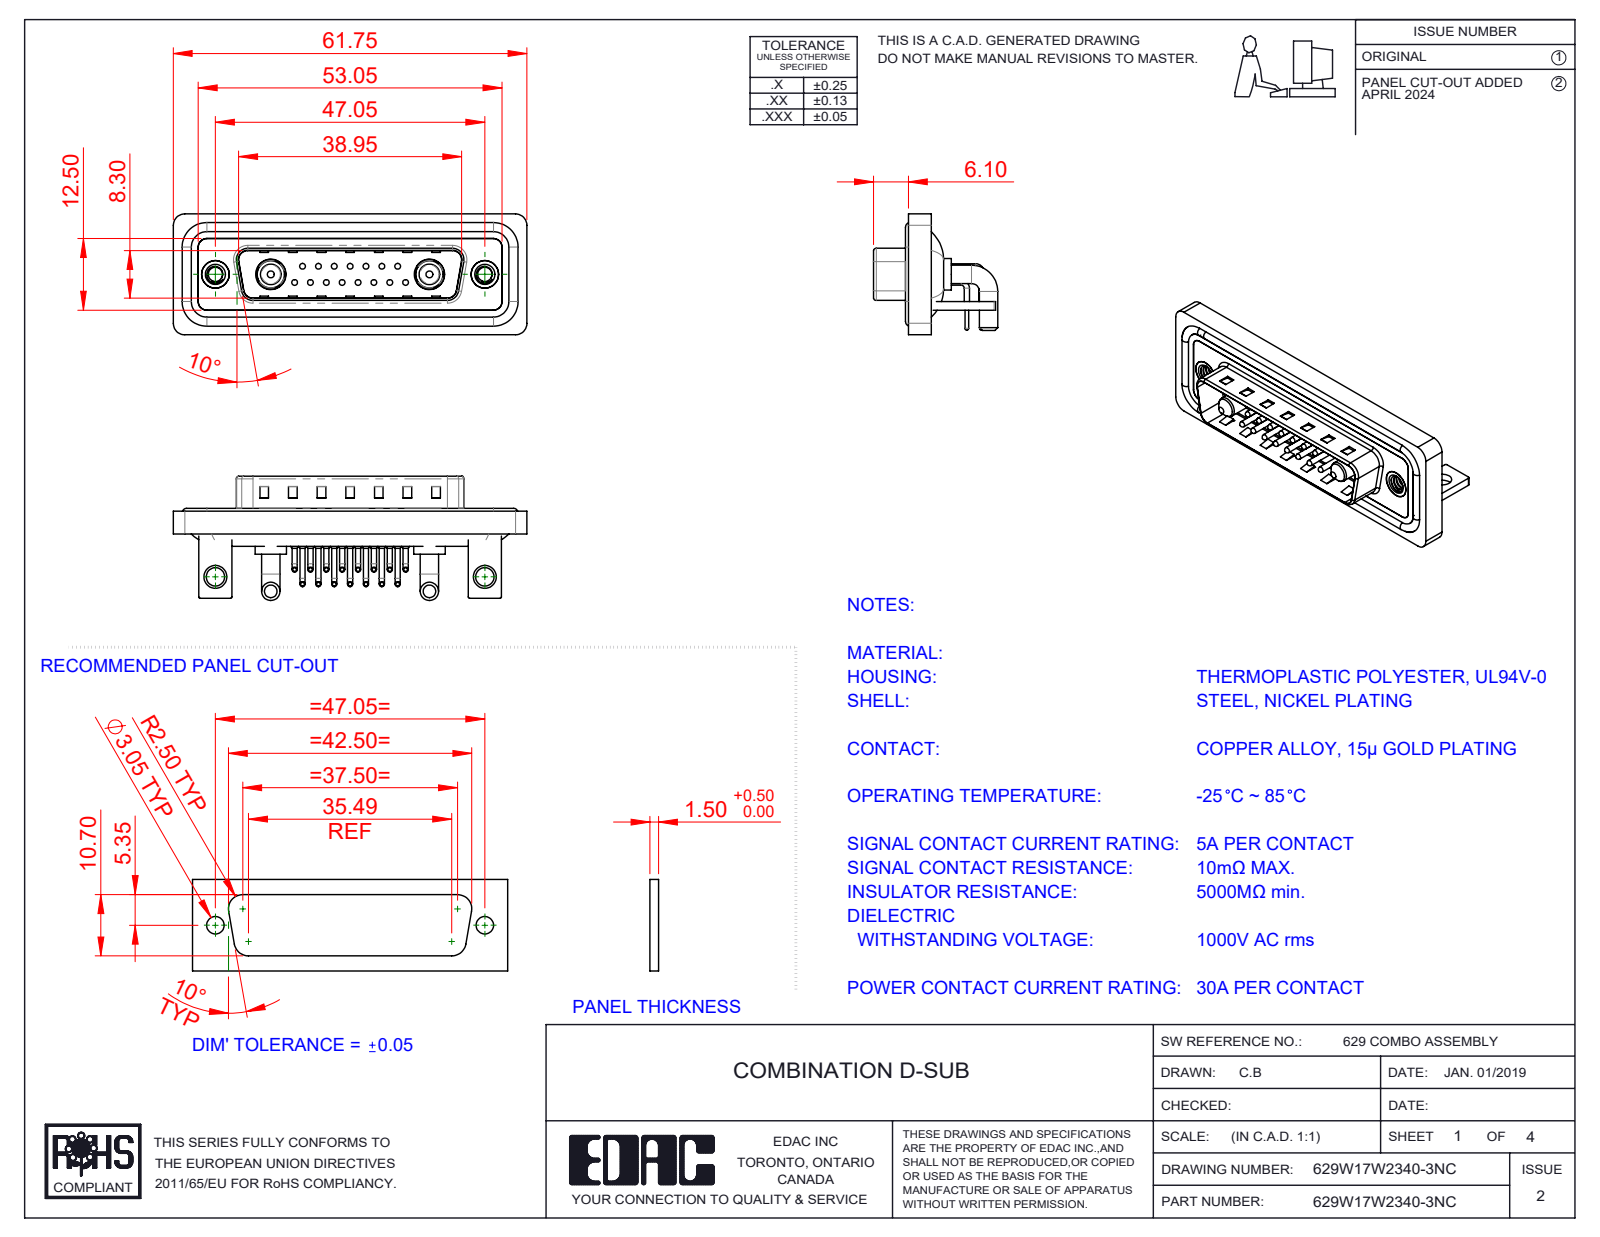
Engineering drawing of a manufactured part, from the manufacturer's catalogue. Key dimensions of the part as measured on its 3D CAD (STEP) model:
Part name (STEP PRODUCT): 629Combo Shell Front_25 Contacts; Power Pin_30A RA; 629Combo Stabilizer Bracket; 629Combo Contact Row 2 (+6 more)
STEP written by: SolidWorks 2023 (CONFIG_CONTROL_DESIGN)
Units: millimetres
Bodies: 28 solids, 2257 faces (1209 planar, 788 cylindrical, 260 other)
Overall size (bounding box): 61.75 × 21.7 × 21.1
Volume: 7 840 mm³ · Surface area: 13 226 mm²
Round holes (diameter × count): ⌀0.75 ×15, ⌀1.6 ×15, ⌀2 ×15, ⌀2.5 ×2, ⌀3.2 ×2, ⌀4 ×2, ⌀4.8 ×2, ⌀4.85 ×2, ⌀5 ×2, ⌀5.3 ×2
Round bosses / shafts (diameter × count): ⌀0.9 ×30, ⌀1.5 ×15, ⌀1 ×15, ⌀0.65 ×15, ⌀3.2 ×4, ⌀1.6 ×4, ⌀5.5 ×2, ⌀5.2 ×2
Partial cylindrical surfaces — rounded edges, fillets, slot ends (radius × count): R2 ×19, R1.5 ×18, R0.25 ×16, R1.01 ×15, R0.5 ×9, R1.6 ×8, R0.6 ×4, R0.65 ×4
Main face-to-face distances: 0.4, 0.8, 1.5, 2.1, 2.9, 1.1, 4.1, 1.6, 4.5, 3.7
Hole centre spacings: 3.16, 2.77, 5.54, 8.31, 5.04, 7.49, 11.08, 5.03
